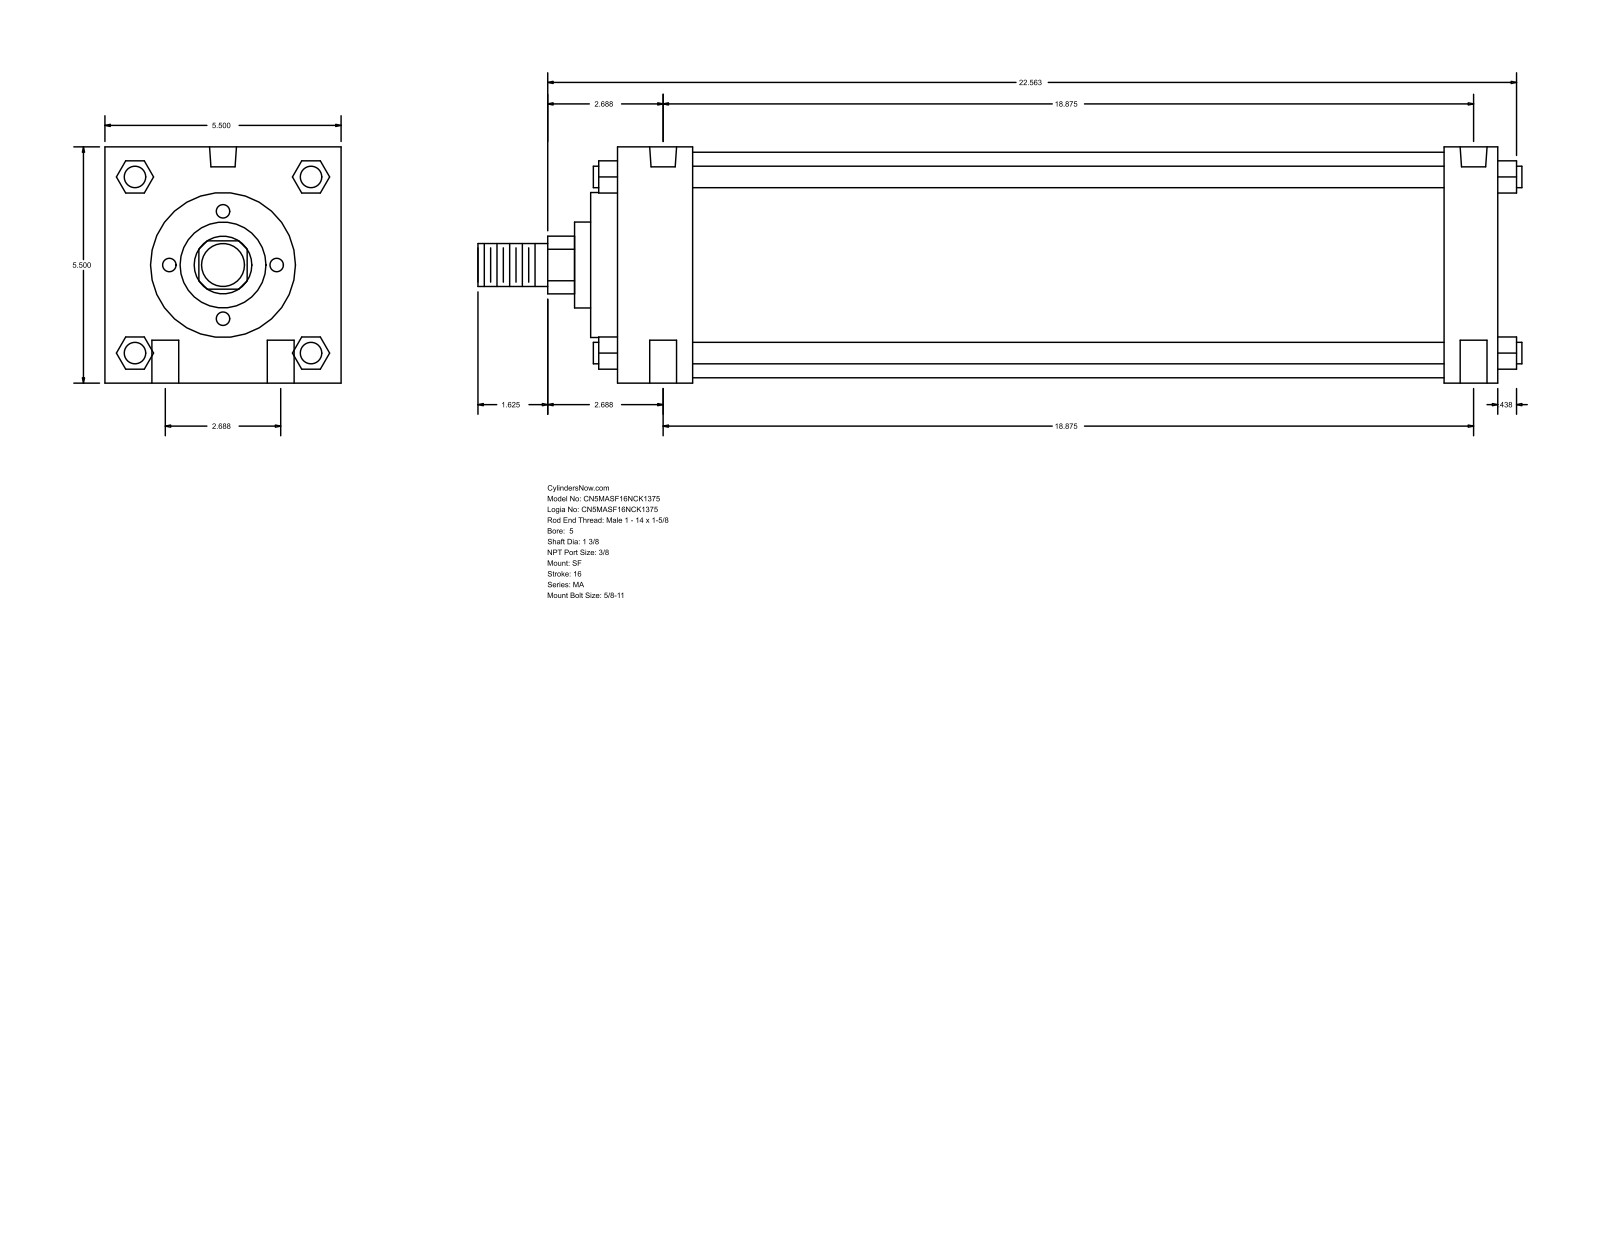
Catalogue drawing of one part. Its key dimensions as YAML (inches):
part_name: "MA_SF__0500_1.375"
step_written_by: "GSSL Pune (CONFIG_CONTROL_DESIGN)"
units: inches
bodies: {solids: 0, faces: 126, planar: 95, cylindrical: 31, other: 0}
overall_size: [24.313, 5.5, 5.5]
round_holes:
  - {diameter: 0.625, count: 4}
  - {diameter: 0.437, count: 2}
  - {diameter: 0.627, count: 2}
round_bosses_or_shafts:
  - {diameter: 0.5, count: 4}
  - {diameter: 5.25, count: 1}
  - {diameter: 3.375, count: 1}
  - {diameter: 2, count: 1}
  - {diameter: 1.375, count: 1}
  - {diameter: 1, count: 1}
partial_cylinders:
  - {radius: 0.672, count: 1}
face_to_face_distances: [5.5, 20.5, 1.75, 19.25, 17.5, 18.75, 1.25, 0.625, 2.375, 19.875]
hole_center_spacings: [1.344, 18.923, 18.875, 2.687, 19.065, 18.5]
